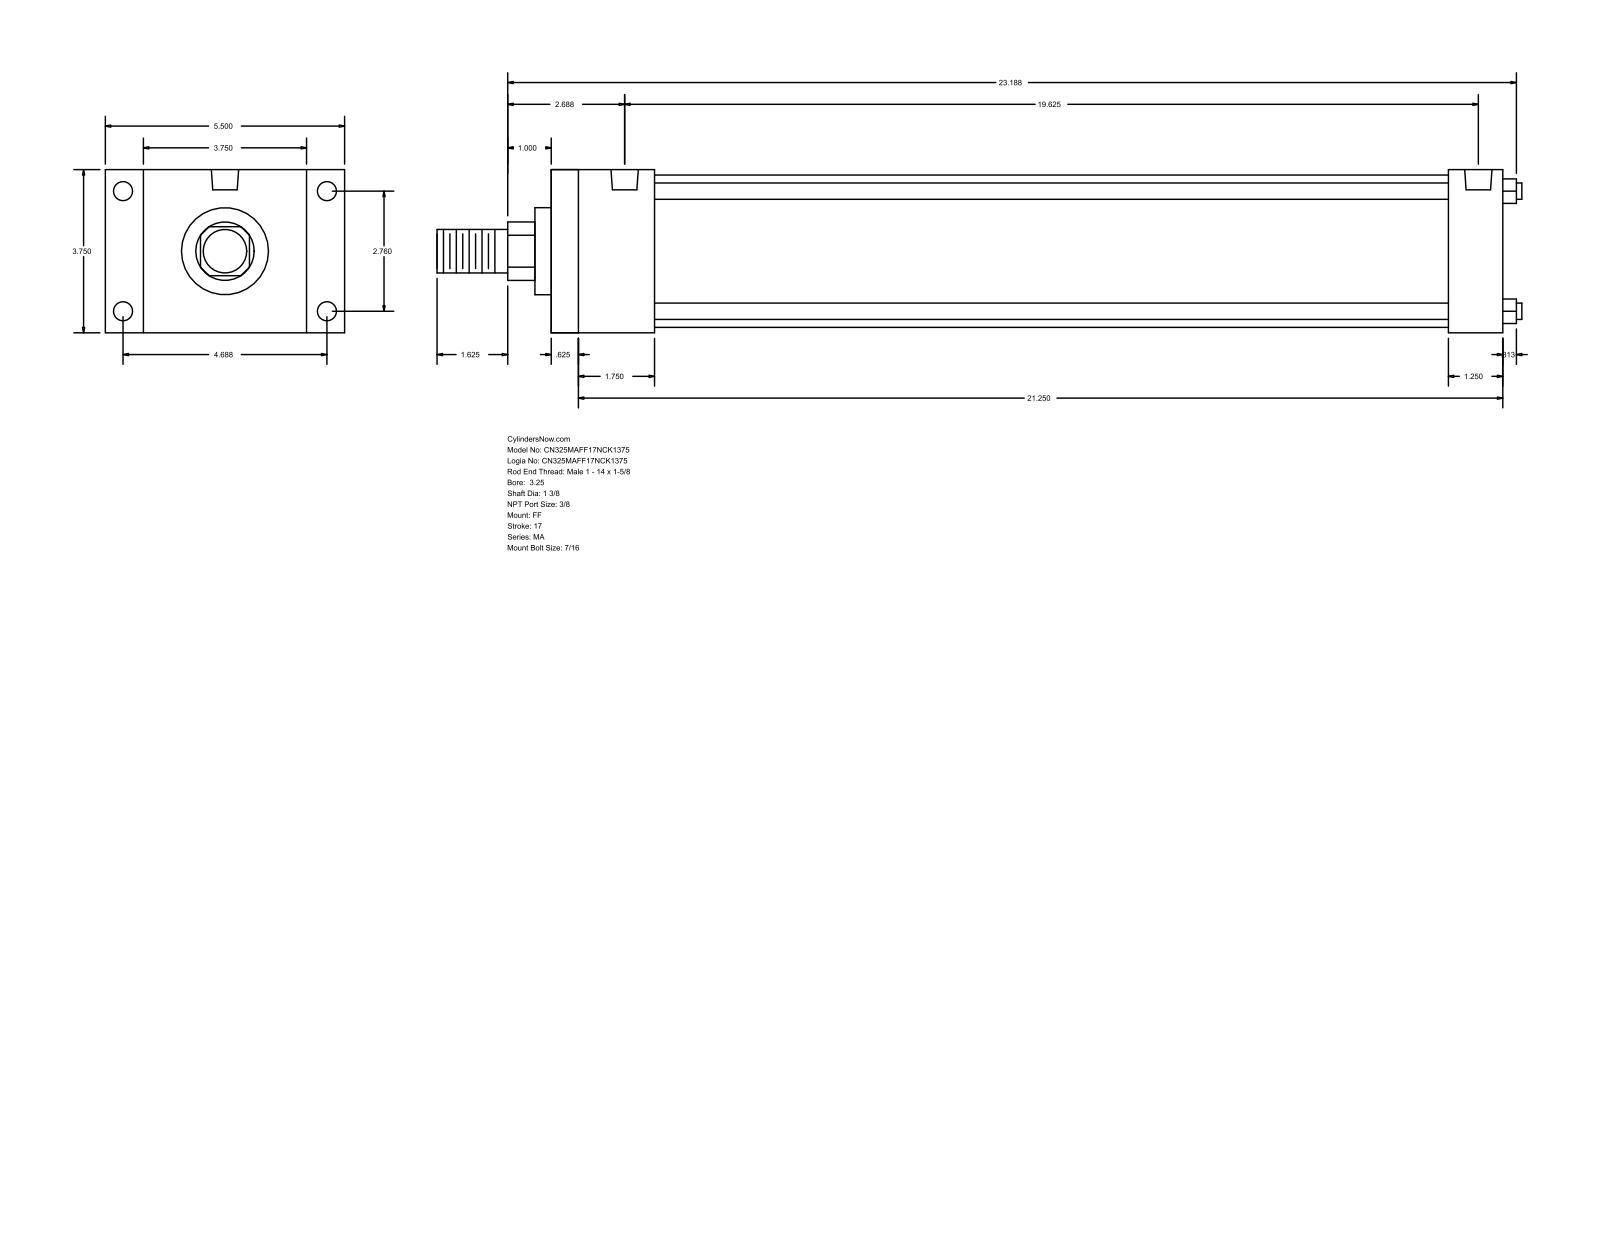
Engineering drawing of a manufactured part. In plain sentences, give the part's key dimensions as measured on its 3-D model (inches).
The part is named "MA_FF__0325_1.375". Its 3-D file was written by "GSSL Pune (CONFIG_CONTROL_DESIGN)". It is 0 solids with 92 faces: 64 planar, 28 cylindrical and 0 other. Overall it measures 24.937 by 5.5 by 3.75 inches. Round holes: 8 of diameter 0.437, 2 of diameter 0.627. Round bosses or shafts: 4 of diameter 0.375, 1 of diameter 3.5, 1 of diameter 2, 1 of diameter 1.375, 1 of diameter 1. Partial cylindrical surfaces (rounded edges, fillets, slot ends): 1 of radius 0.672. The main face-to-face distances are 3.75, 21.875, 0.625, 21.25, 0.875, 4.625, 2.375, 20.625, 1.75, 20. The hole center spacings are 2.76, 4.687, 5.439, 19.25, 0.187, 0.188, 19.437, 19.438.
